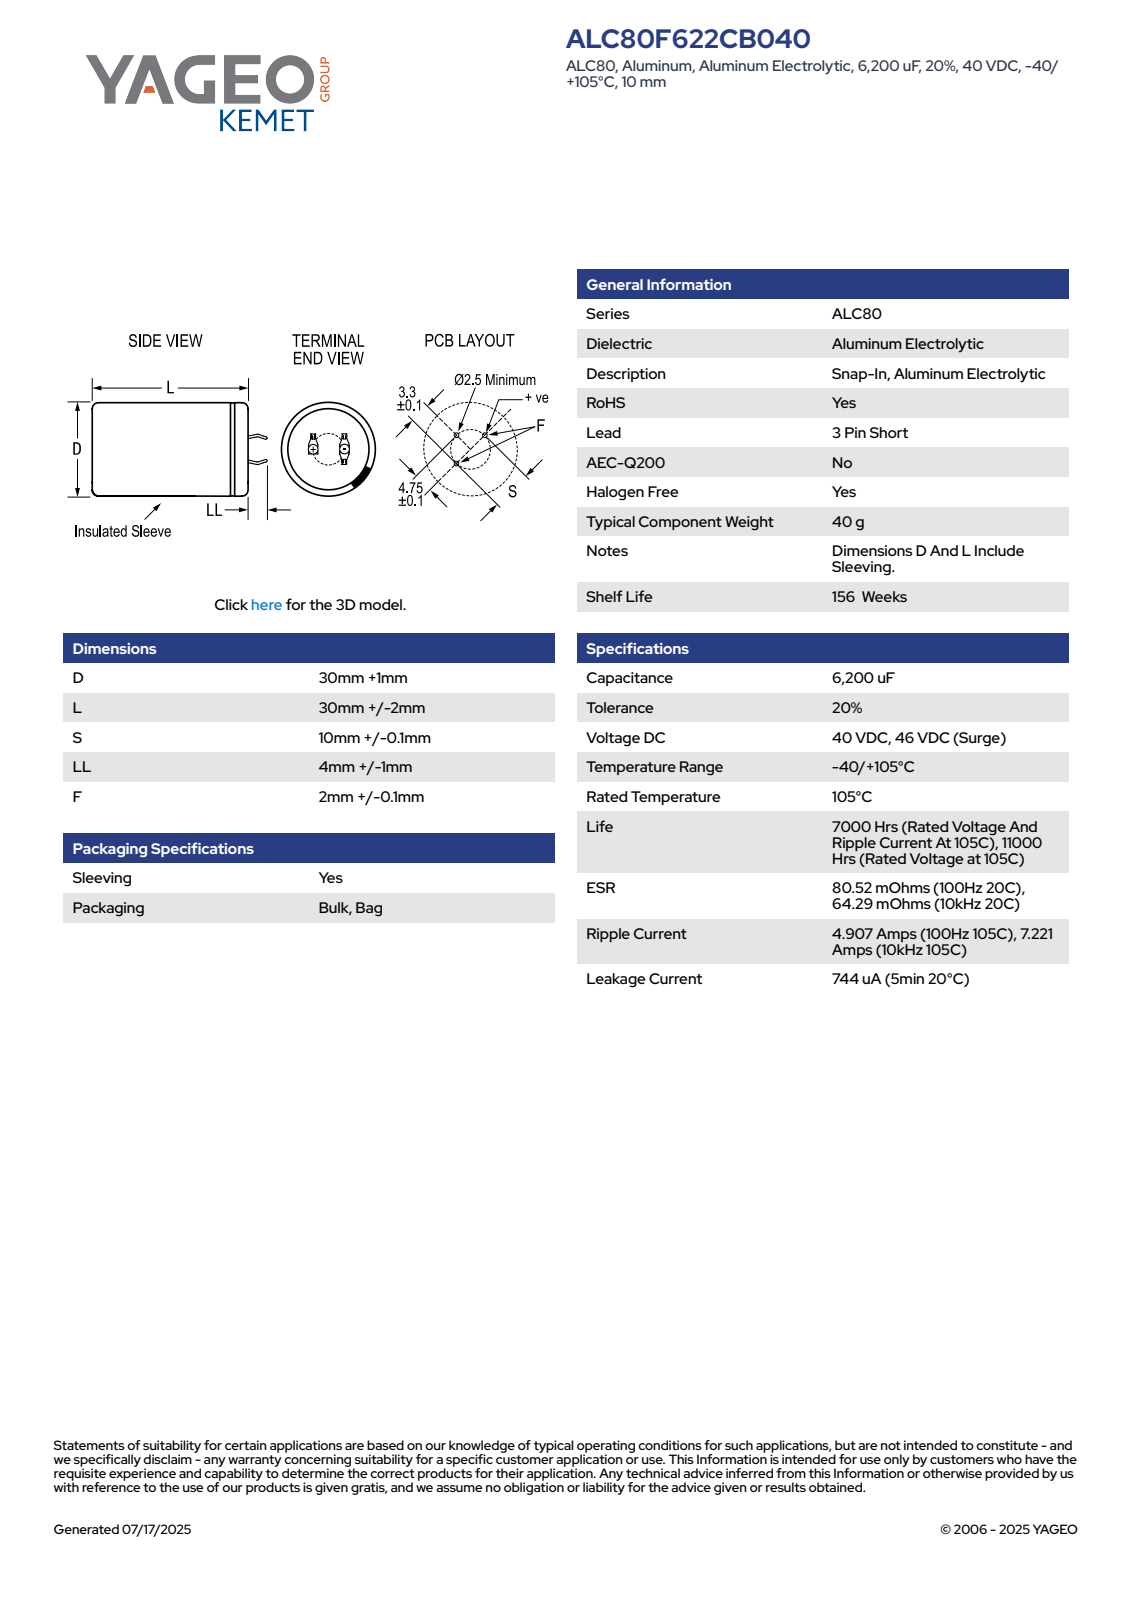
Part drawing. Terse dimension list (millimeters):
name: CARS_K3P_30X30_D31L32S10LL5F2.1
written by: SolidWorks 2014 (AUTOMOTIVE_DESIGN)
unit: mm
bodies: 1 solid, 115 faces (61 planar, 15 cylindrical, 39 other)
size: 36.99 × 31 × 31
volume: 23 819 mm³; area: 4 636 mm²
holes: 1× ⌀27.43
bosses: 1× ⌀31
rounds: 1× R15.49
face distances: 31.99, 32.49, 0.5, 0.6, 8.22, 0.59, 0.75, 1.35, 6.51, 8.97
